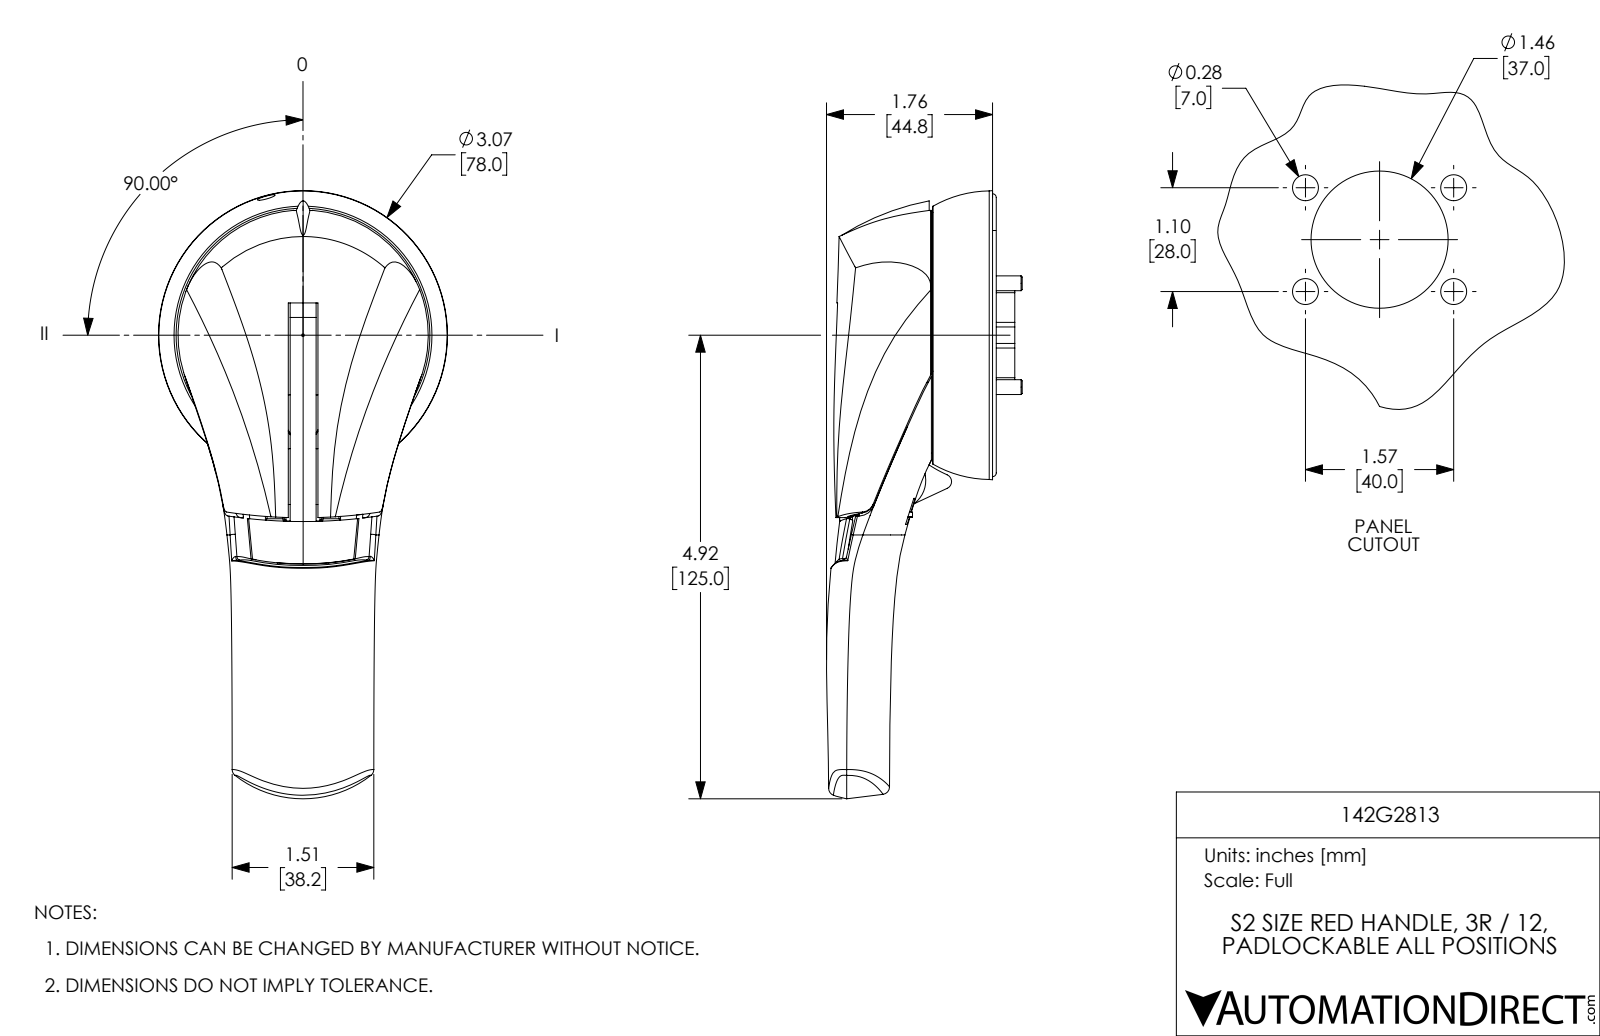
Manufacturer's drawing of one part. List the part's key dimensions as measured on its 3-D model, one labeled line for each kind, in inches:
Part name (STEP PRODUCT): 142G2813
STEP written by: SolidWorks 2017 (AUTOMOTIVE_DESIGN)
Units: inches
Bodies: 8 solids, 1516 faces (810 planar, 548 cylindrical, 158 other)
Overall size (bounding box): 6.458 × 3.07 × 2.079
Volume: 9.514 in³ · Surface area: 87.31 in²
Round holes (diameter × count): ⌀0.157 ×6, ⌀0.339 ×4, ⌀0.425 ×4, ⌀0.03 ×3, ⌀0.169 ×2, ⌀0.362 ×2, ⌀0.118 ×1, ⌀0.189 ×1, ⌀2.992 ×1
Round bosses / shafts (diameter × count): ⌀0.02 ×11, ⌀0.335 ×4, ⌀0.315 ×4, ⌀0.089 ×3, ⌀0.069 ×3, ⌀0.228 ×2, ⌀2.819 ×1, ⌀2.701 ×1
Partial cylindrical surfaces — rounded edges, fillets, slot ends (radius × count): R0.01 ×221, R0.015 ×20, R0.034 ×20, R0.03 ×15, R0.039 ×4, R0.025 ×3, R5.437 ×3, R0.079 ×2
Main face-to-face distances: 0.024, 0.701, 0.713, 0.689, 0.035, 0.102, 0.276, 0.173, 0.244, 0.047
Hole centre spacings: 0.961, 0.309, 0.669, 1.098, 1.102, 1.203, 1.575, 1.881
